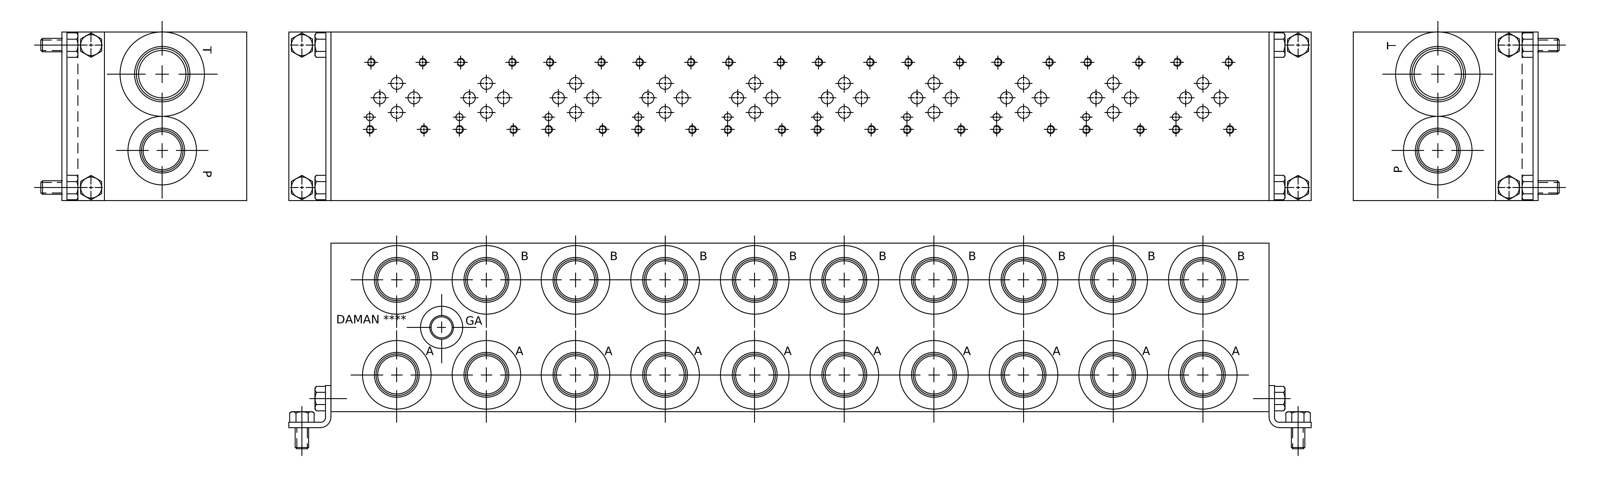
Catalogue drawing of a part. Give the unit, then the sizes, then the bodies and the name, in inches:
Units: inches
Overall size (bounding box): 22.25 × 4 × 4
Round holes (diameter × count): ⌀0.149 ×40, ⌀0.19 ×40, ⌀0.25 ×30, ⌀0.906 ×21, ⌀0.981 ×21, ⌀1.08 ×21, ⌀1.655 ×21, ⌀1.063 ×20, ⌀0.422 ×11, ⌀0.156 ×10, ⌀0.281 ×10, ⌀0.257 ×2
Main face-to-face distances: 4, 0.031, 3.969, 22.25, 22.219, 0.781, 0.75, 3.219, 22.188, 0.039
Hole centre spacings: 4.25, 8.5, 2.125, 2.125, 3.095, 6.375, 12.75, 4.809
Volume: 327.2 in³ · Surface area: 511.9 in²
Bodies: 1 solid, 1385 faces (640 planar, 274 cylindrical, 471 other)
Part name (STEP PRODUCT): Part_AD03HP102S_3D
STEP written by: Autodesk Inventor 2019 (AUTOMOTIVE_DESIGN)
